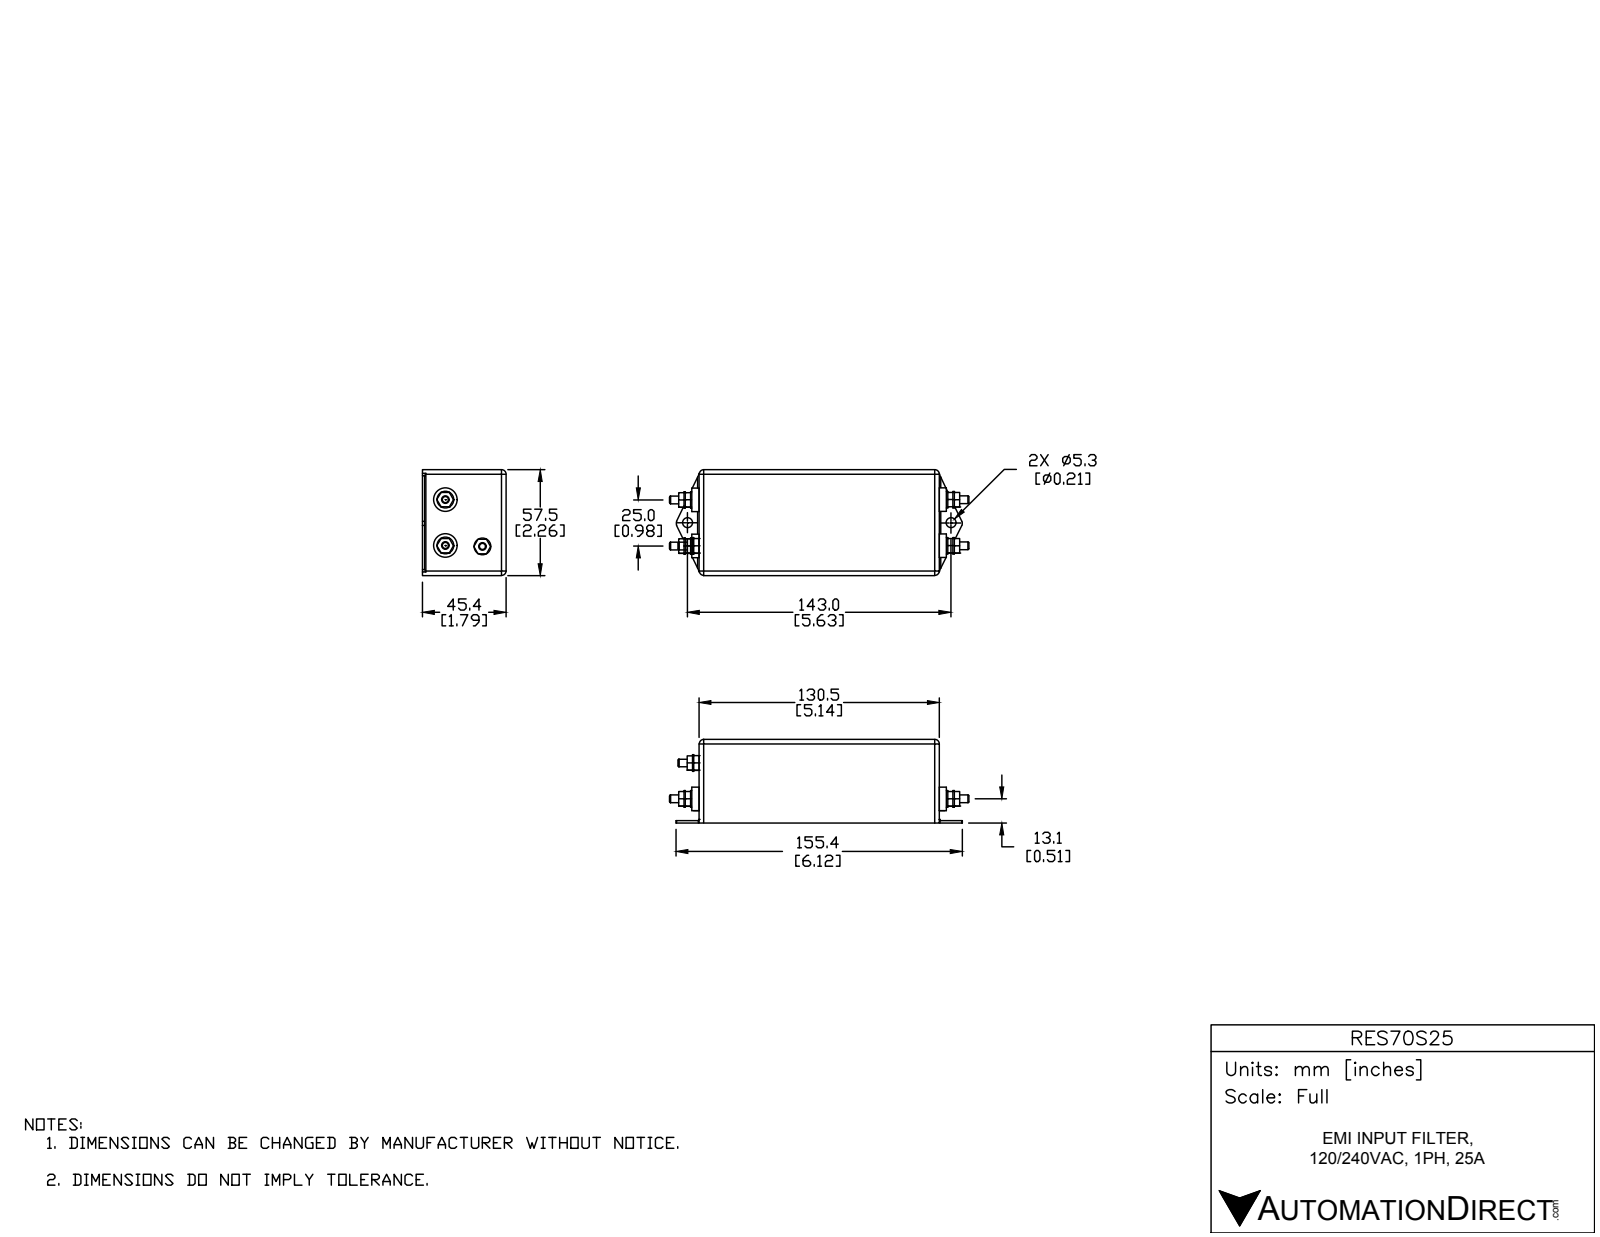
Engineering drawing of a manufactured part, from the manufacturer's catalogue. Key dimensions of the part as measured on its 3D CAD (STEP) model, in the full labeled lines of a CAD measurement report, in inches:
Part name (STEP PRODUCT): RES70S25
STEP written by: SolidWorks 2015 (AUTOMOTIVE_DESIGN)
Units: inches
Bodies: 1 solid, 52 faces (17 planar, 29 cylindrical, 6 other)
Overall size (bounding box): 6.122 × 2.264 × 1.787
Volume: 21.32 in³ · Surface area: 51.39 in²
Round holes (diameter × count): ⌀0.209 ×2, ⌀0.079 ×1
Round bosses / shafts (diameter × count): ⌀0.504 ×2
Partial cylindrical surfaces — rounded edges, fillets, slot ends (radius × count): R0.197 ×12, R0.098 ×2, R0.03 ×1
Main face-to-face distances: 1.787, 2.264, 5.276, 0.15, 5.425, 0.047, 1.74, 5.575, 5.421, 5.272
Hole centre spacings: 5.63
